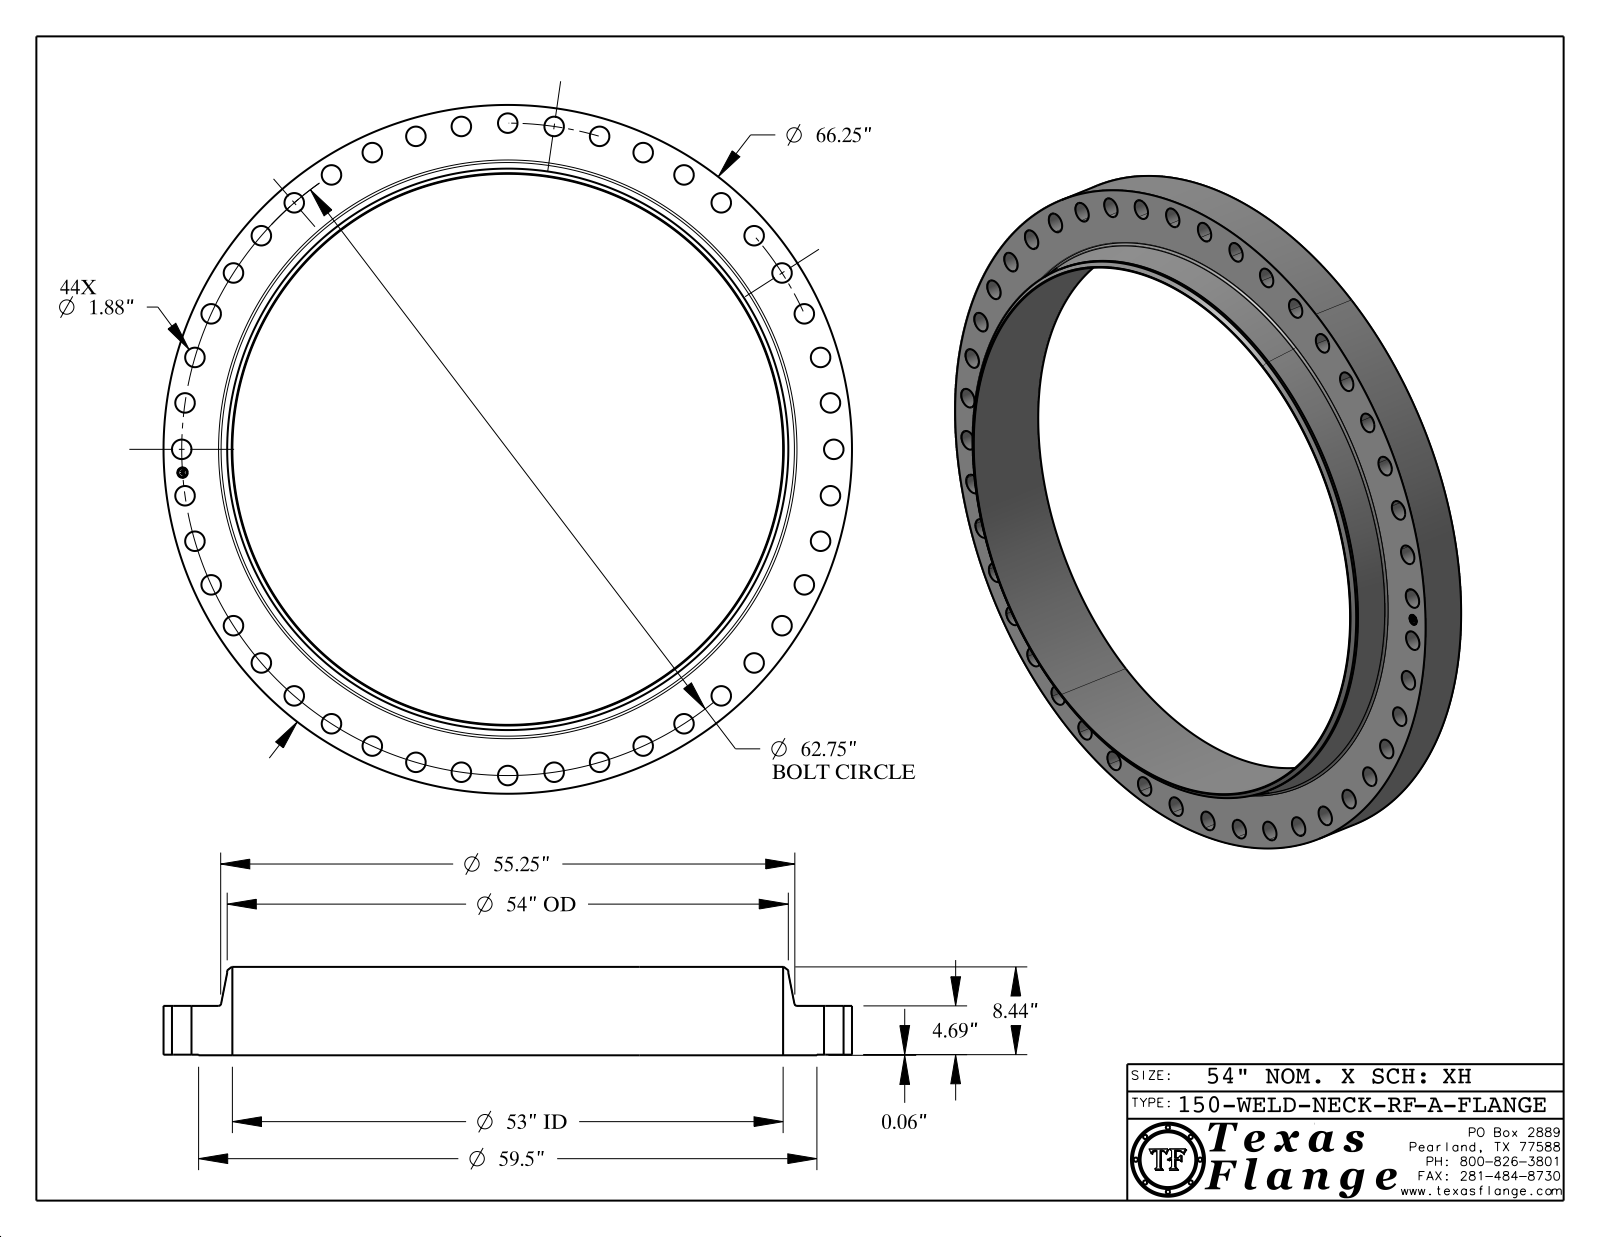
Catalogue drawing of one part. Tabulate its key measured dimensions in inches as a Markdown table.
| quantity | value |
| --- | --- |
| part name | 150-WELD-NECK-RF, Series A |
| STEP written by | CATIA V5 STEP AP214 (AUTOMOTIVE_DESIGN) |
| units | inches |
| bodies | 1 solid, 491 faces (369 planar, 116 cylindrical, 6 other) |
| overall size | 66.25 × 66.25 × 8.503 |
| volume | 5 758 in³ |
| surface area | 6 357 in² |
| round holes (diameter × count) | 1.88 × 44, 1 × 1, 53 × 1 |
| round bosses / shafts (diameter × count) | 0.061 × 8, 66.25 × 1, 59.5 × 1, 54 × 1, 0.788 × 1 |
| main face-to-face distances | 4.753, 0.063, 4.69, 8.503, 8.44, 3.75, 0.015, 4.738, 4.675, 3.765 |
| hole center spacings | 62.59, 62.111, 31.375, 61.316, 4.476, 8.93, 21.929, 13.338 |
